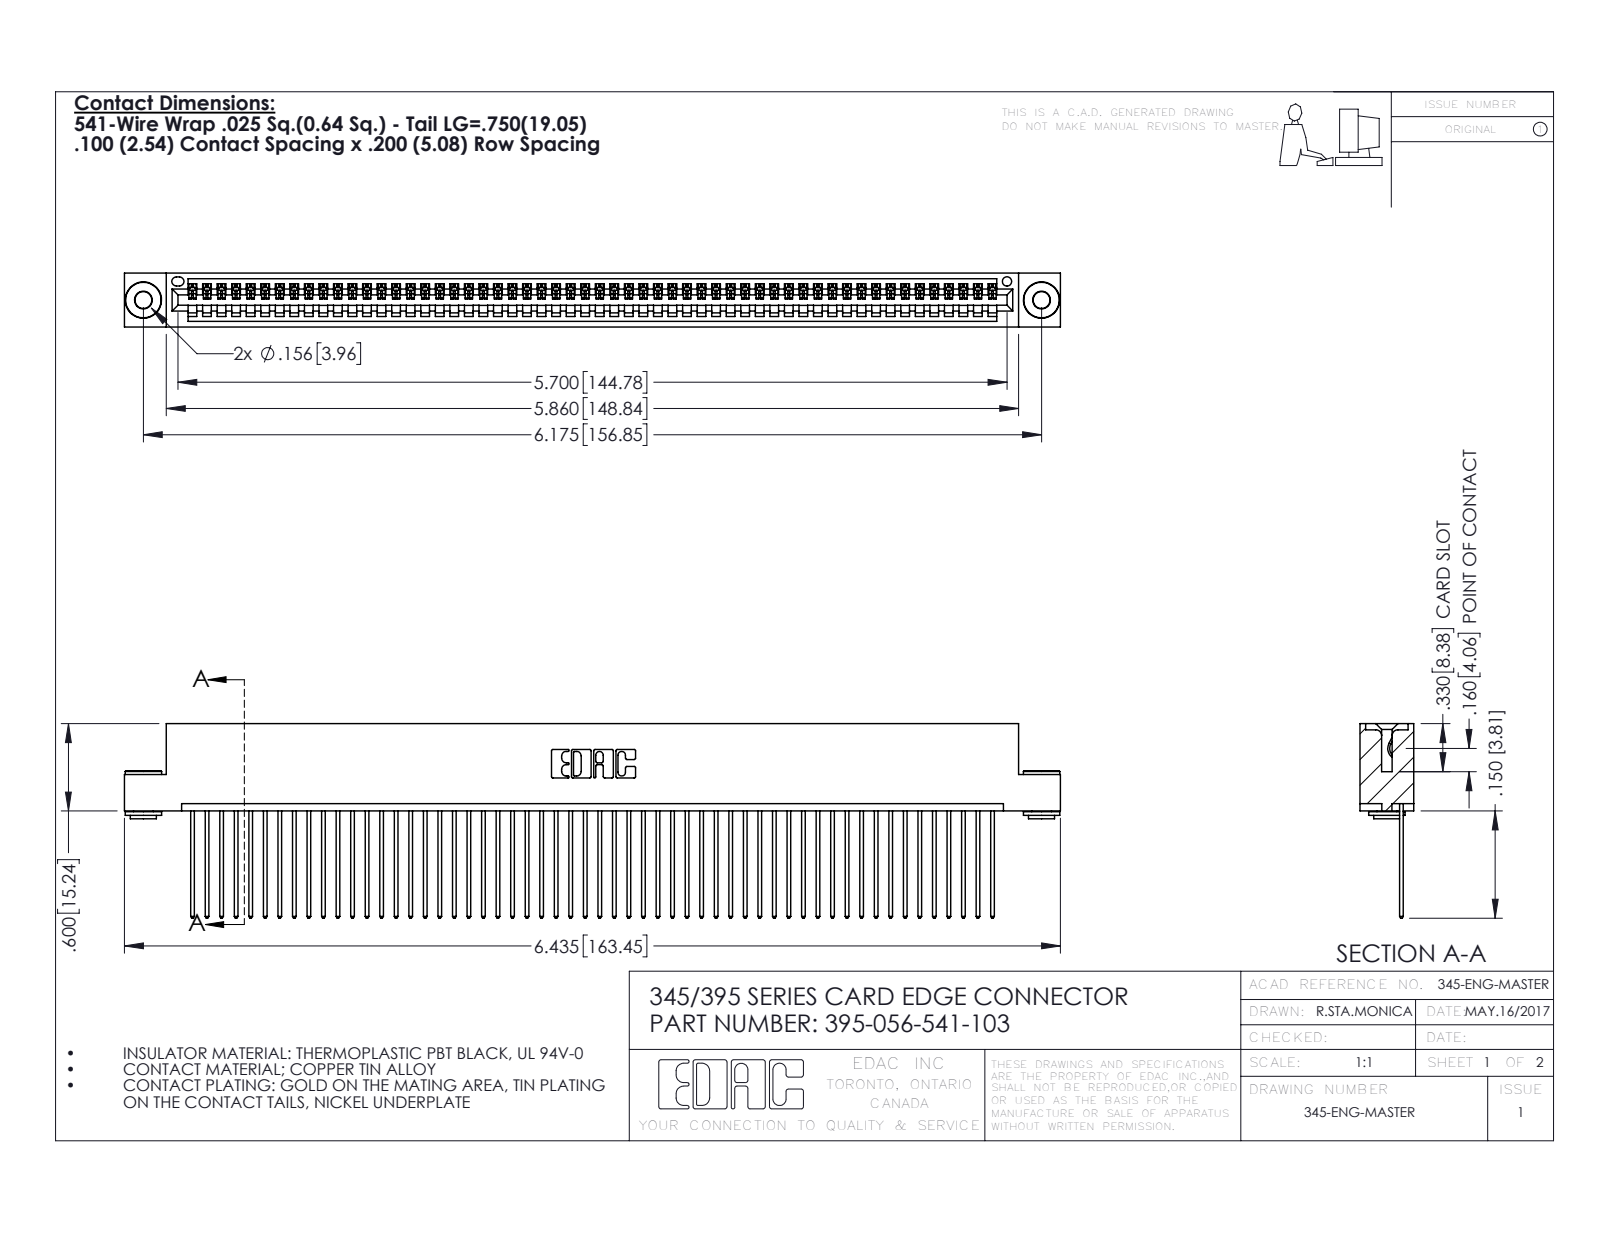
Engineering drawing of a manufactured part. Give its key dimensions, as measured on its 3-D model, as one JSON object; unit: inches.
{"part_name": "395-056-541-103; 345-250-002_345-250-002-102; 345-292-001_345-293-141; 345 Part_Flush Mounting Lugs - 0.156 Dia-TH", "step_written_by": "SolidWorks 2016 (CONFIG_CONTROL_DESIGN)", "units": "inches", "bodies": {"solids": 59, "faces": 3412, "planar": 2330, "cylindrical": 1074, "other": 8}, "overall_size": [6.435, 1.337, 0.37], "volume_in3": 0.967, "surface_area_in2": 34.95, "round_holes": [[0.116, 2], [0.156, 2], [0.064, 1]], "round_bosses_or_shafts": [[0.25, 2], [0.18, 2], [0.136, 2]], "partial_cylinders_radius": [[0.006, 112], [0.01, 112], [0.01, 22], [0.007, 6], [0.031, 6], [0.026, 3], [0.031, 2], [0.04, 2]], "face_to_face_distances": [0.072, 0.298, 0.025, 0.098, 0.272, 0.37, 0.2, 0.225, 0.149, 0.072], "hole_center_spacings": [0.27, 5.939, 6.175]}
